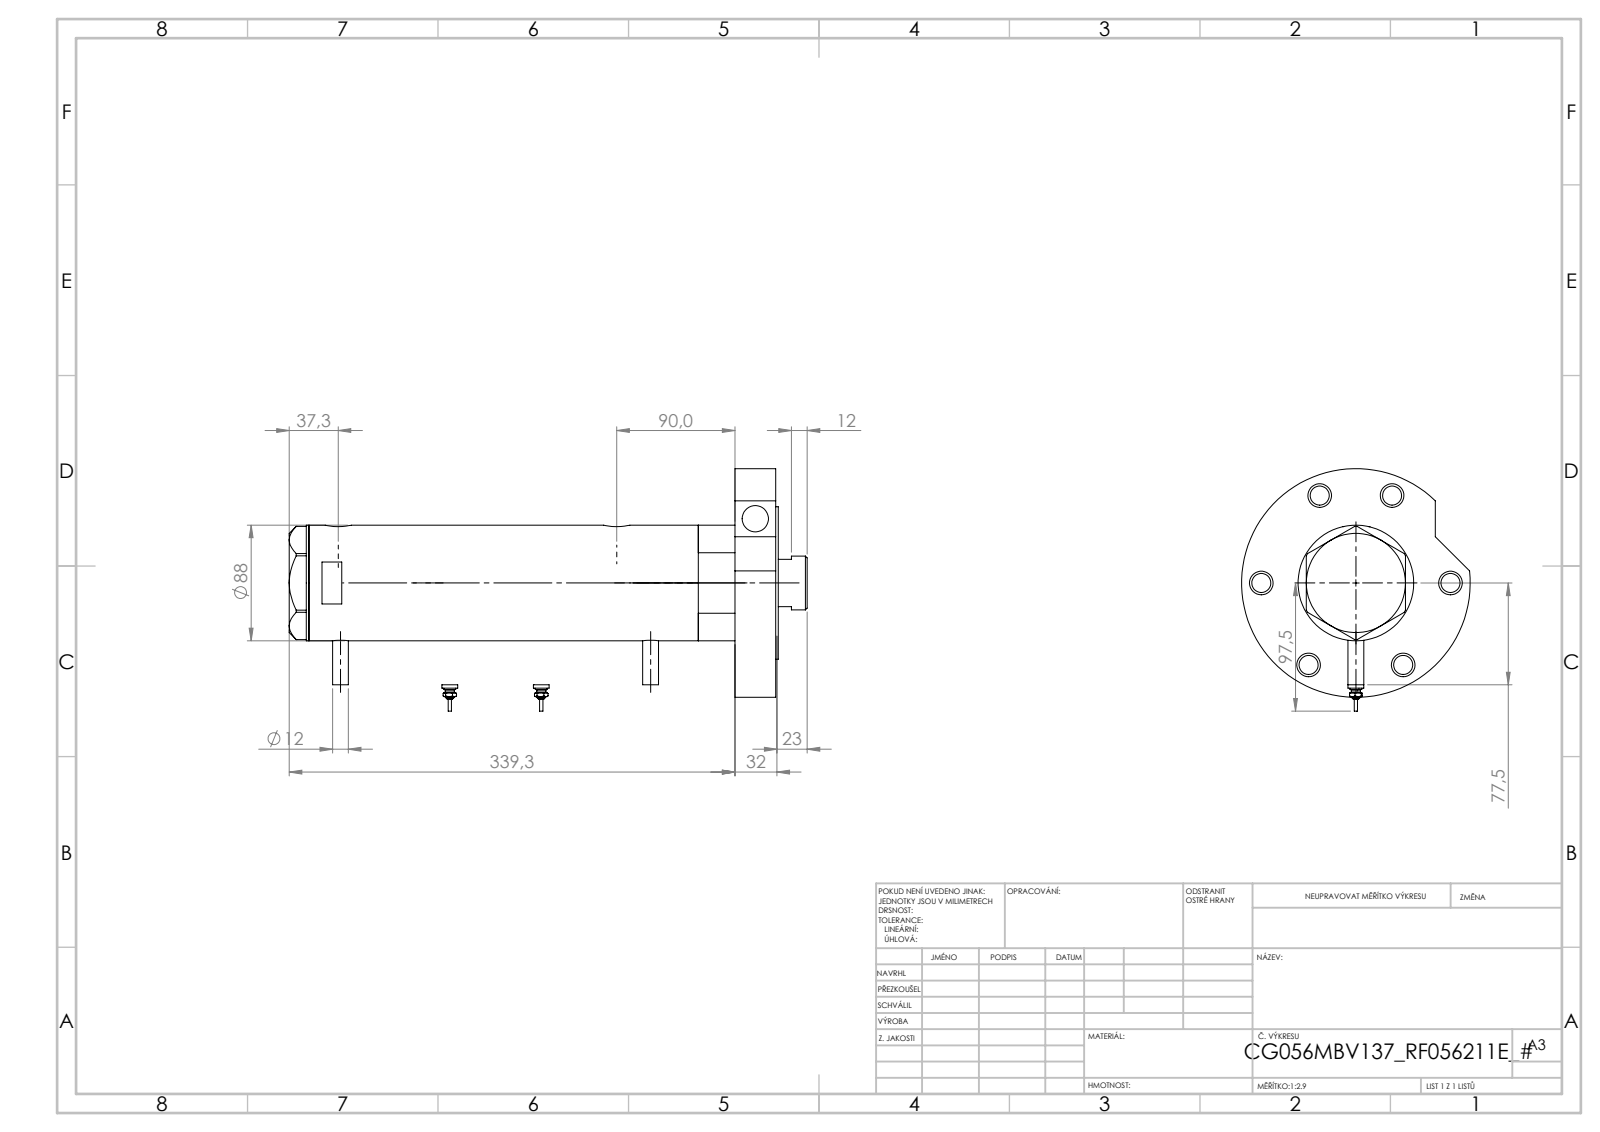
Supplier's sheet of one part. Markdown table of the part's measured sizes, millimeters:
| quantity | value |
| --- | --- |
| part name | V270CG_FRONT; V270CG_VC; Switch; V270CG_BACK (+2 more) |
| STEP written by | SolidWorks 2019 (CONFIG_CONTROL_DESIGN) |
| units | millimeters |
| bodies | 7 solids, 257 faces (91 planar, 102 cylindrical, 64 other) |
| overall size | 394.3 × 184.5 × 174 |
| volume | 2 575 000 mm³ |
| surface area | 361 263 mm² |
| round holes (diameter × count) | 14.5 × 7, 18 × 6, 20 × 3, 12.5 × 2, 13.16 × 2, 42 × 1, 43.5 × 1, 56 × 1, 60 × 1, 75 × 1, 80 × 1 |
| round bosses / shafts (diameter × count) | 12 × 4, 9 × 2, 7 × 2, 4.5 × 2, 2.5 × 2, 174 × 1, 116 × 1, 88 × 1 |
| main face-to-face distances | 31, 2, 357.3, 324.3, 355.3, 33, 234.4, 89.9, 120.9, 122.9 |
| hole center spacings | 72, 80, 119.73, 124.71, 129.15, 143.69, 1.7, 25.8 |
